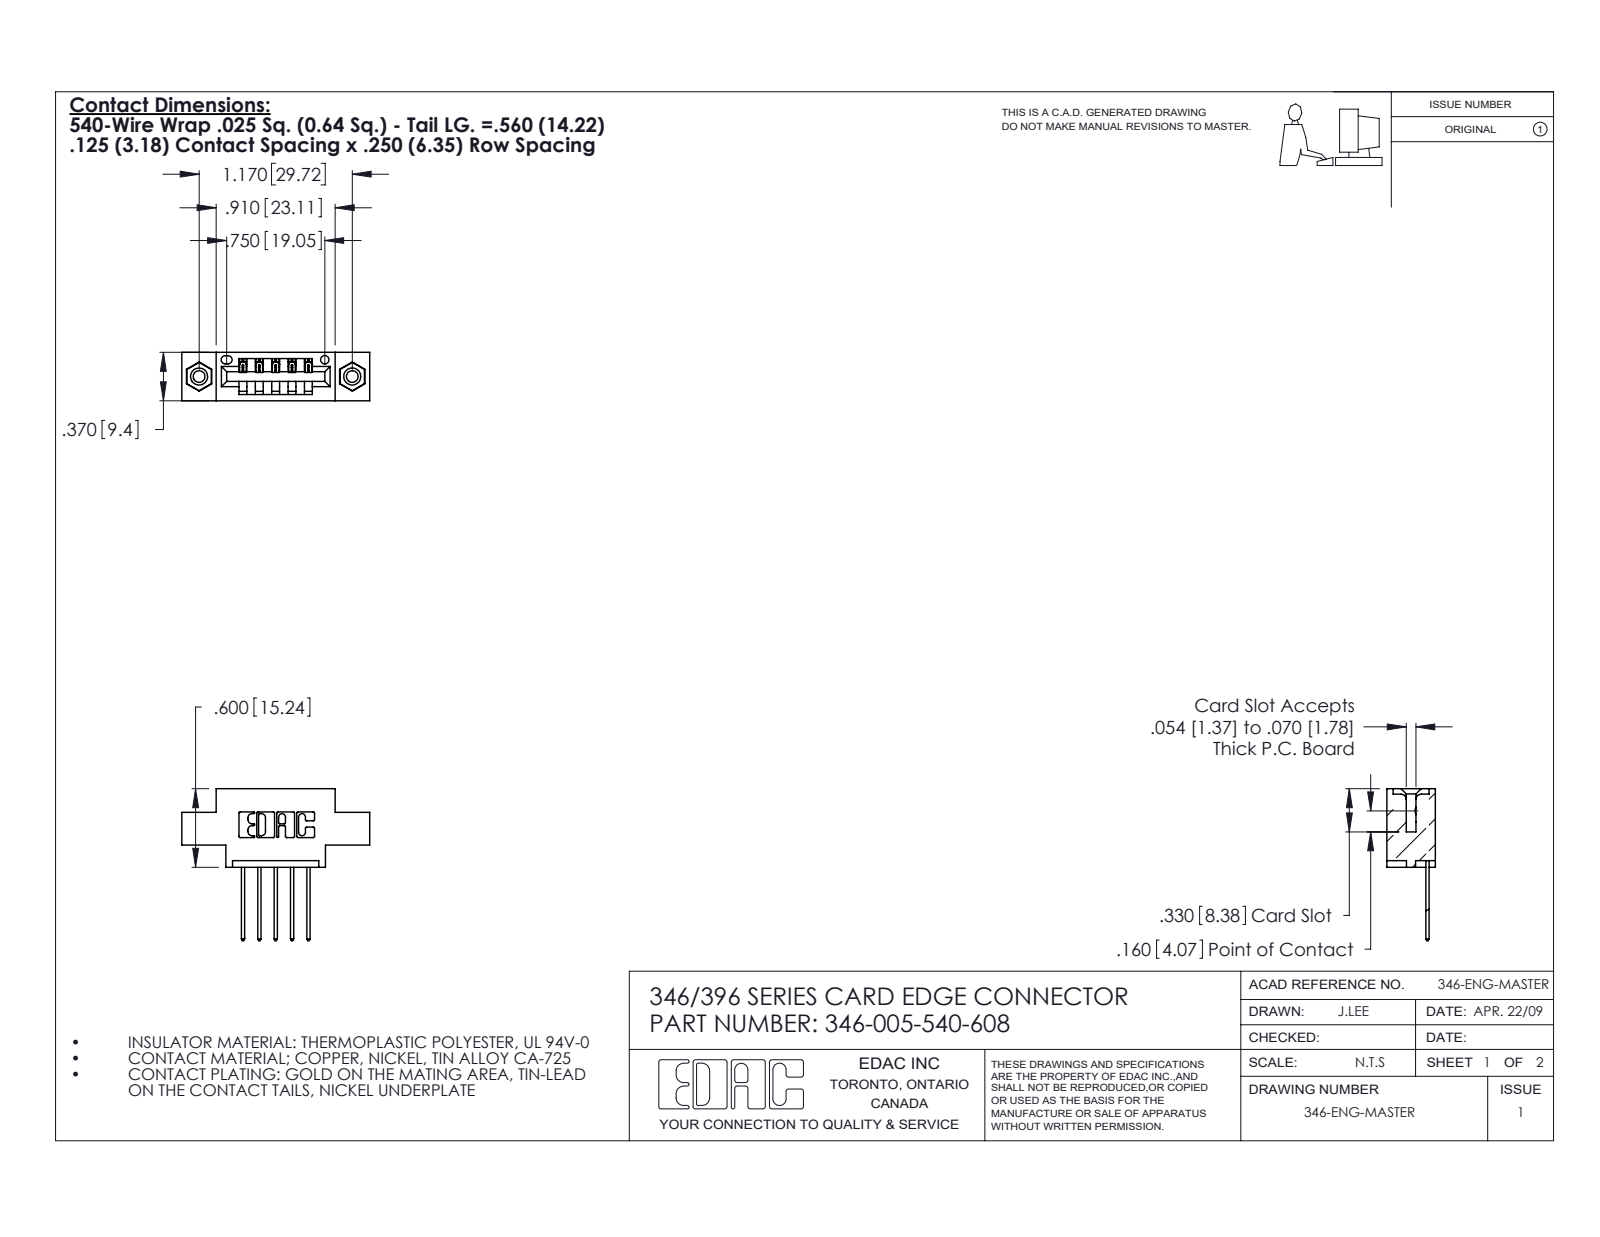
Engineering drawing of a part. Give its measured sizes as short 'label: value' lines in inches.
name: 345-250-001_345-250-003-102; 345-292-001_345-293-140; 346-005-540-608; 346 Part_0.170 Offset - 0.156 Dia-TI
written by: SolidWorks 2020 (CONFIG_CONTROL_DESIGN)
unit: in
bodies: 8 solids, 476 faces (312 planar, 148 cylindrical, 16 other)
size: 1.435 × 1.16 × 0.37
volume: 0.188 in³; area: 5.706 in²
holes: 2× ⌀0.089, 2× ⌀0.125, 2× ⌀0.156, 1× ⌀0.064
bosses: 2× ⌀0.155
rounds: 22× R0.01, 10× R0.006, 10× R0.01, 6× R0.007, 6× R0.031, 3× R0.026, 2× R0.031, 2× R0.04
face distances: 0.25, 0.37, 0.048, 0.322, 0.222, 0.148, 0.072, 0.298, 0.025, 0.1
hole spacings: 0.246, 0.969, 1.17
